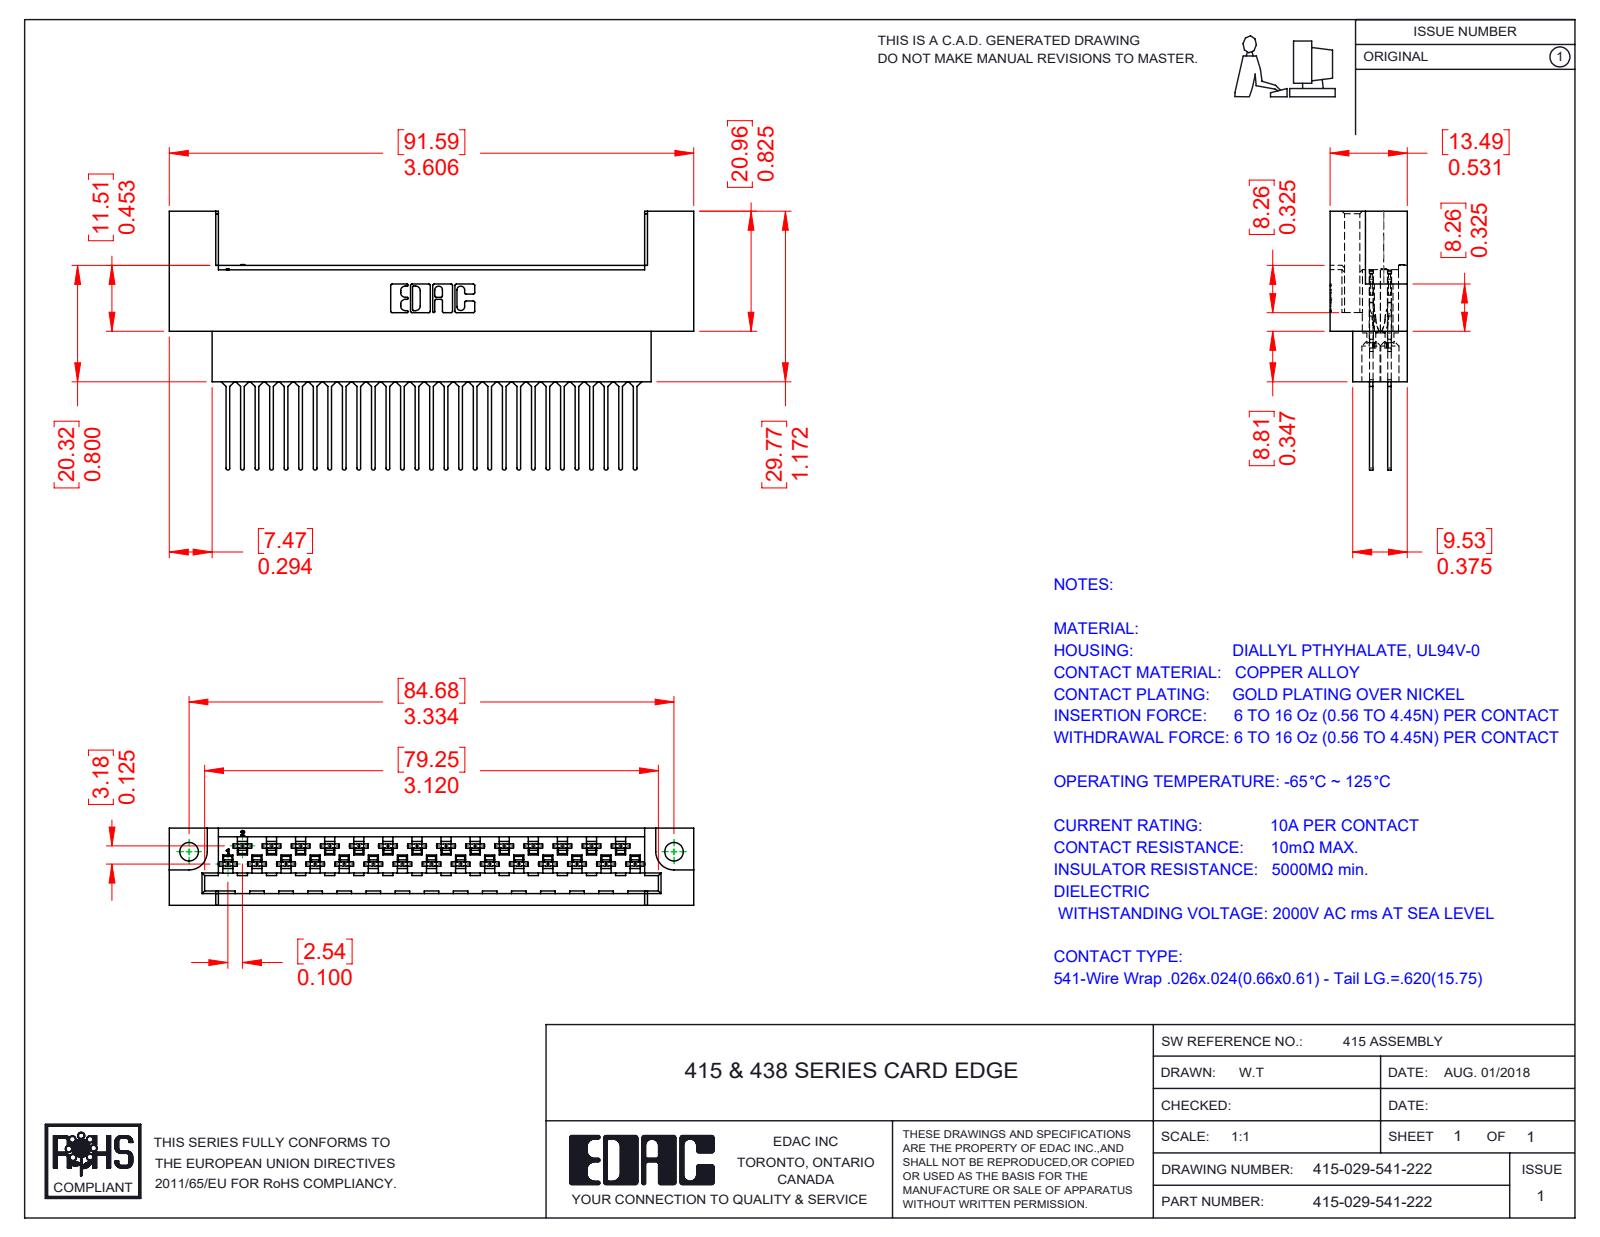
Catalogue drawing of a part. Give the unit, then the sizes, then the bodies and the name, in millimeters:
Units: millimetres
Overall size (bounding box): 91.59 × 45.17 × 13.49
Round holes (diameter × count): ⌀1.27 ×29, ⌀3.3 ×29, ⌀3.25 ×2
Partial cylindrical surfaces — rounded edges, fillets, slot ends (radius × count): R0.3 ×116, R0.56 ×116, R0.18 ×58, R0.2 ×58, R0.41 ×58, R2.03 ×58, R0.33 ×29, R0.25 ×22
Main face-to-face distances: 3.18, 0.61, 13.49, 7.49, 1.27, 1.88, 6.61, 6.88, 6, 2.82
Hole centre spacings: 5.08, 10.16, 15.24, 20.32, 25.4, 30.48, 35.56, 2.54
Volume: 15 946 mm³ · Surface area: 20 248 mm²
Bodies: 30 solids, 3002 faces (1919 planar, 800 cylindrical, 283 other)
Part name (STEP PRODUCT): 516-290-001_541; 415-029-541-222; 415-210-001_415-210-029-222
STEP written by: SolidWorks 2016 (CONFIG_CONTROL_DESIGN)
